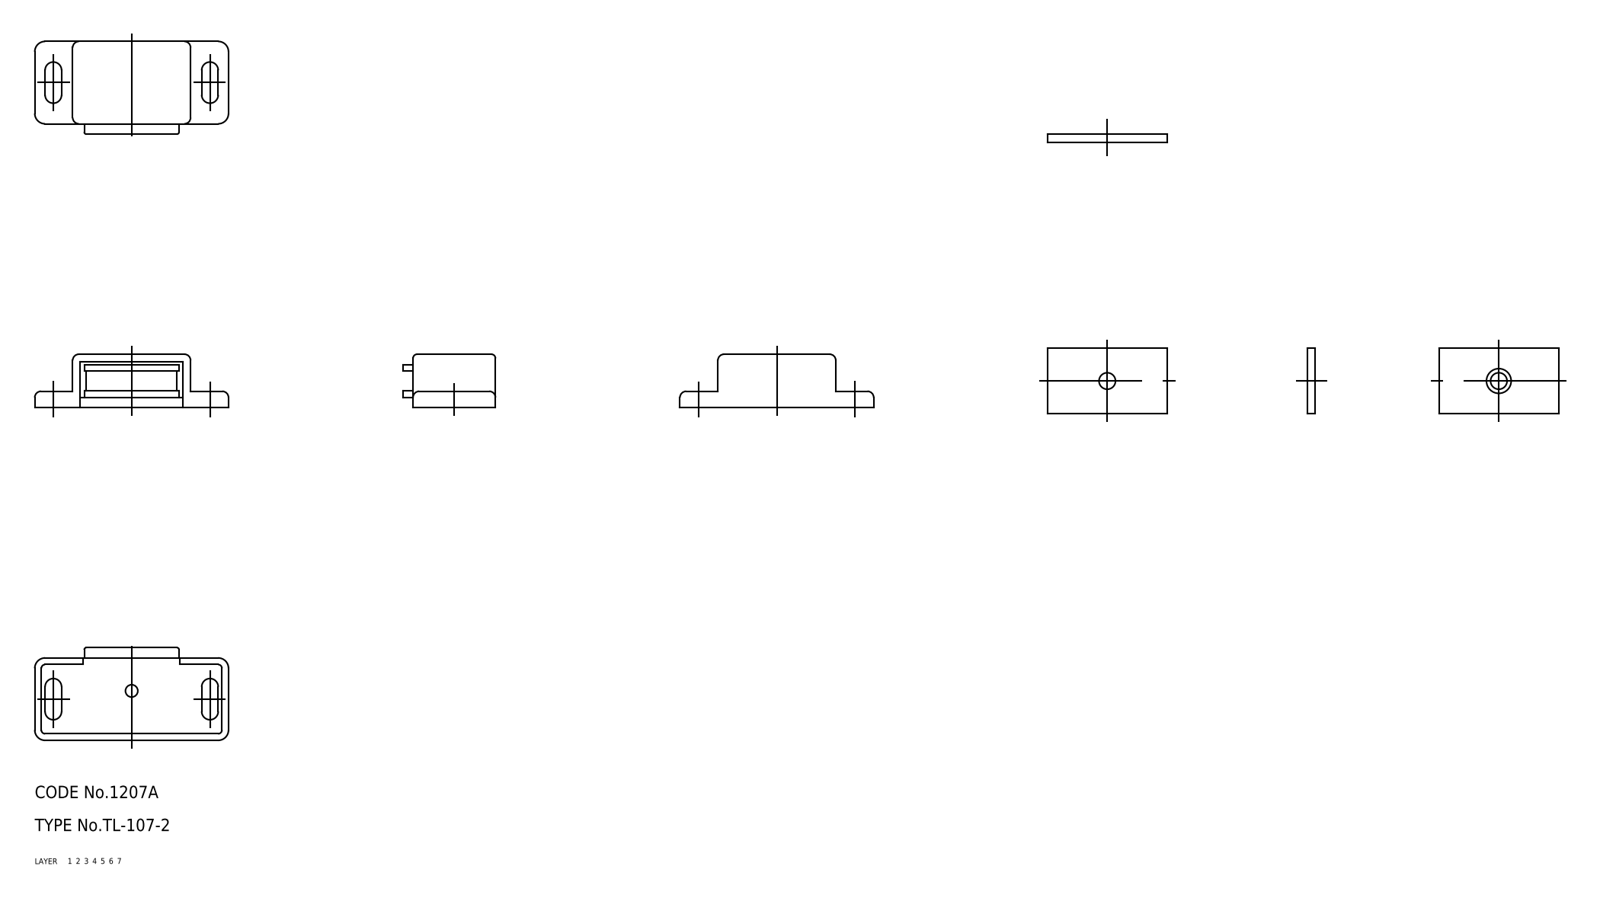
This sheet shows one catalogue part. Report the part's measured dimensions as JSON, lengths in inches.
{"part_name": "67113814; 67113827; 67113840; 67113853 (+2 more)", "step_written_by": "CADfix (AUTOMOTIVE_DESIGN)", "units": "inches", "bodies": {"solids": 6, "faces": 125, "planar": 0, "cylindrical": 0, "other": 125}, "overall_size": [2.106, 1.85, 0.63], "volume_in3": 0.543, "surface_area_in2": 15.27}
